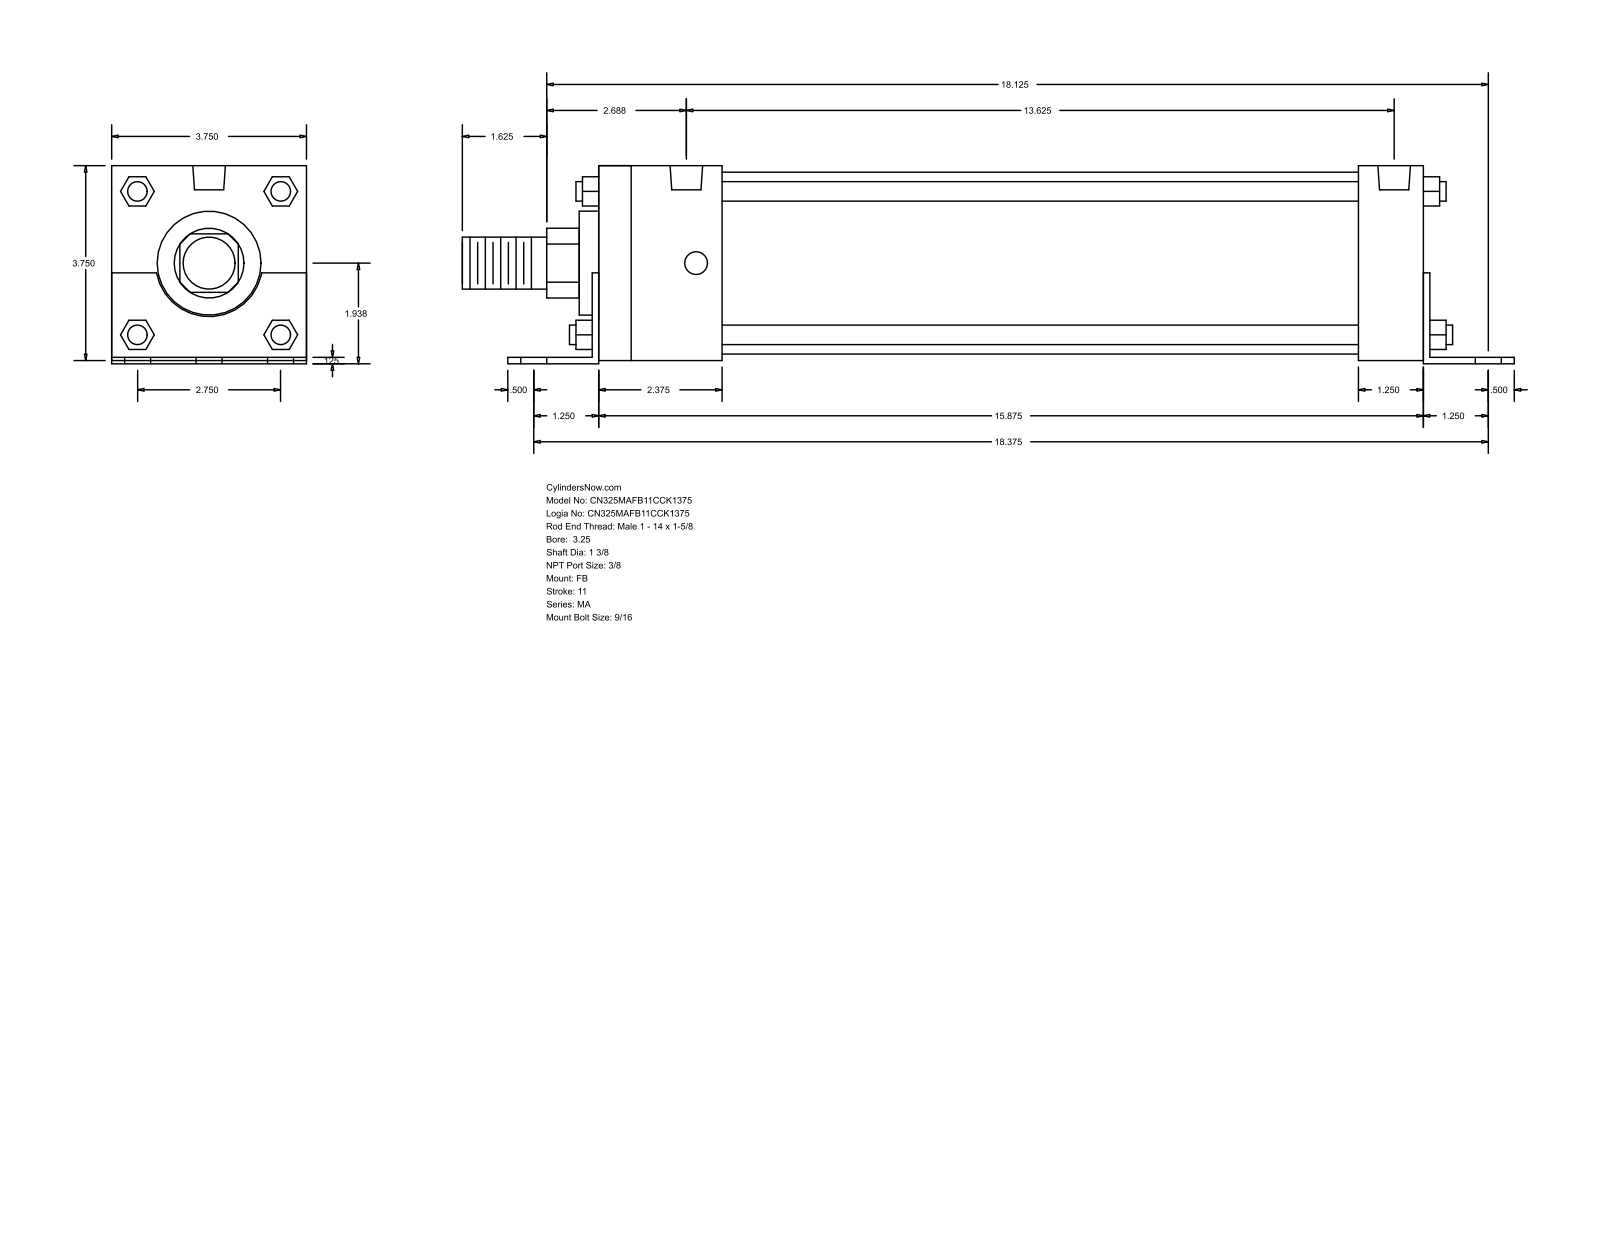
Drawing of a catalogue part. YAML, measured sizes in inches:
part_name: "MA_FB__0325_1.375"
step_written_by: "GSSL Pune (CONFIG_CONTROL_DESIGN)"
units: inches
bodies: {solids: 0, faces: 140, planar: 105, cylindrical: 35, other: 0}
overall_size: [20.25, 3.813, 3.75]
round_holes:
  - {diameter: 0.563, count: 6}
  - {diameter: 0.437, count: 4}
  - {diameter: 0.627, count: 2}
round_bosses_or_shafts:
  - {diameter: 0.375, count: 4}
  - {diameter: 3.5, count: 1}
  - {diameter: 2, count: 1}
  - {diameter: 1.375, count: 1}
  - {diameter: 1, count: 1}
partial_cylinders:
  - {radius: 0.672, count: 1}
  - {radius: 1.03, count: 1}
face_to_face_distances: [3.75, 0.125, 0.063, 3.812, 0.062, 3.687, 0.125, 15.875, 16, 1.375]
hole_center_spacings: [1.375, 18.426, 18.375, 0.188, 2.275, 2.427, 2.75, 3.243]
